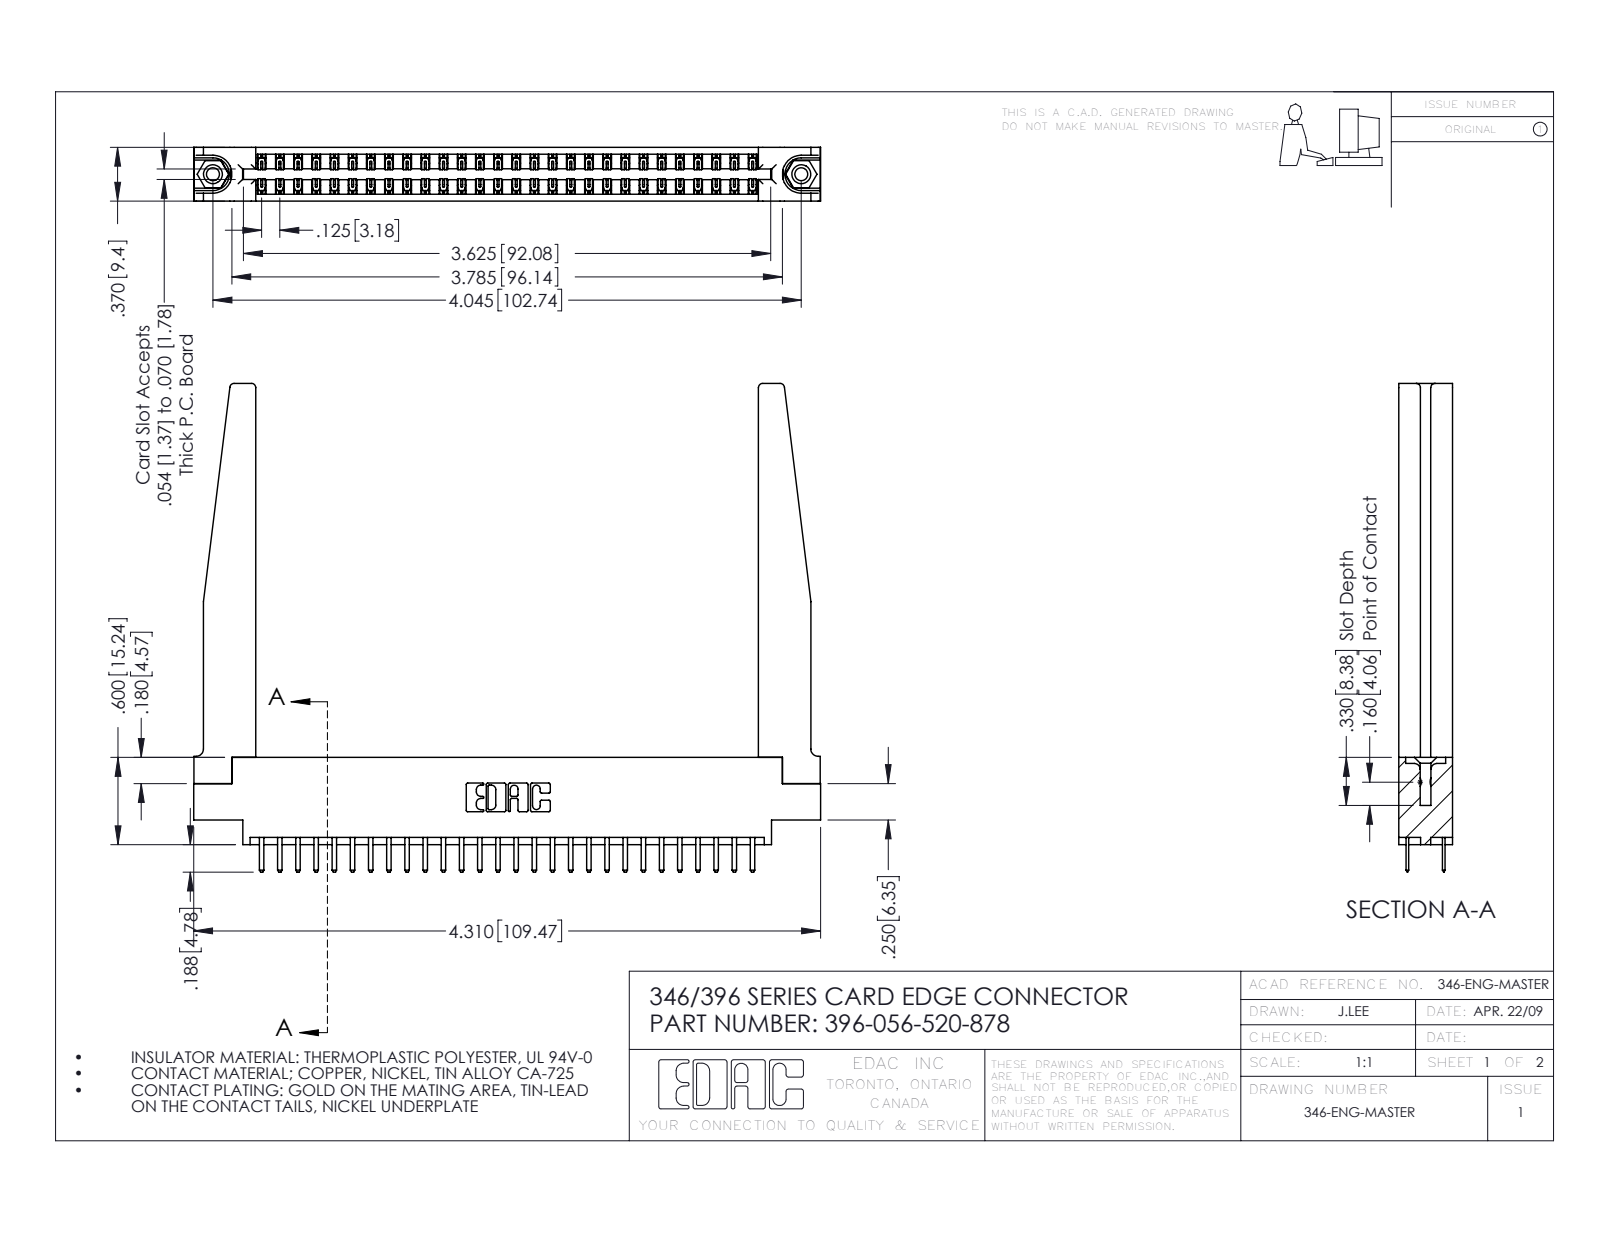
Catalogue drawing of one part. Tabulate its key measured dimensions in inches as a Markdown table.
| quantity | value |
| --- | --- |
| part name | 396-056-520-878; 345-250-001_345-250-001-102; 346 Part_0.170 Offset - 0.156 Dia-TH; 345-292-001_345-293-120 (+1 more) |
| STEP written by | SolidWorks 2016 (CONFIG_CONTROL_DESIGN) |
| units | inches |
| bodies | 61 solids, 3496 faces (2294 planar, 1150 cylindrical, 52 other) |
| overall size | 4.31 × 3.358 × 0.37 |
| volume | 1.055 in³ |
| surface area | 32.11 in² |
| round holes (diameter × count) | 0.089 × 2, 0.125 × 2, 0.156 × 2, 0.064 × 1 |
| round bosses / shafts (diameter × count) | 0.155 × 2 |
| partial cylindrical surfaces (radius × count) | 0.006 × 84, 0.01 × 60, 0.01 × 22, 0.03 × 8, 0.007 × 6, 0.031 × 6, 0.026 × 3, 0.014 × 2 |
| main face-to-face distances | 0.37, 0.048, 0.322, 0.072, 0.25, 0.15, 0.148, 0.298, 0.025, 0.275 |
| hole center spacings | 0.246, 3.837, 4.045 |
